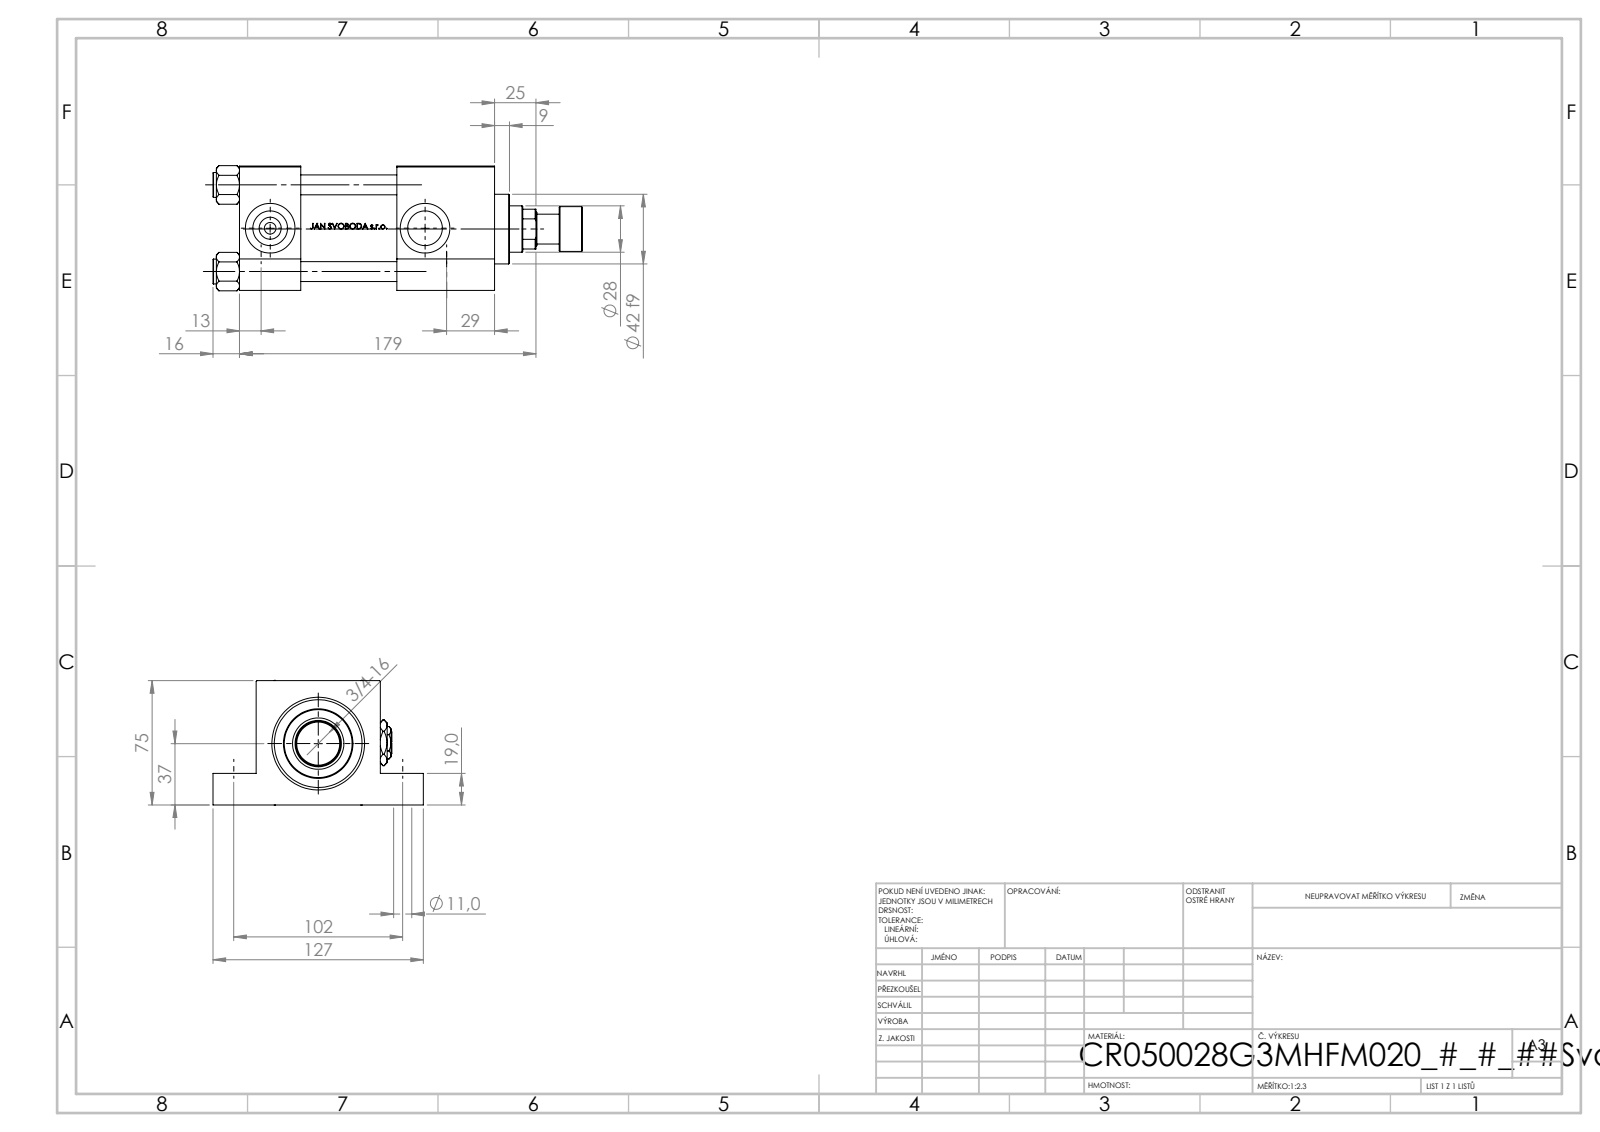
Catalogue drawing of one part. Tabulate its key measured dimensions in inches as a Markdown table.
| quantity | value |
| --- | --- |
| part name | Zatka_pro_OIL_PORT; V215CR_VCP_G; V215CR_ROD_END_F; NUT_M5_G (+3 more) |
| STEP written by | SolidWorks 2019 (CONFIG_CONTROL_DESIGN) |
| units | inches |
| bodies | 14 solids, 1197 faces (481 planar, 136 cylindrical, 580 other) |
| overall size | 8.78 × 5 × 2.974 |
| volume | 47.23 in³ |
| surface area | 264.8 in² |
| round holes (diameter × count) | 0.472 × 4, 0.433 × 3, 0.276 × 2, 0.825 × 2, 1.181 × 2, 0.433 × 1, 0.728 × 1, 1.102 × 1, 1.22 × 1, 1.614 × 1, 1.969 × 1, 2.087 × 1 |
| round bosses / shafts (diameter × count) | 0.591 × 4, 2.205 × 1, 1.654 × 1, 1.063 × 1, 0.709 × 1 |
| main face-to-face distances | 2.953, 1.457, 6.063, 4.606, 0.748, 2.205, 3.74, 2.283, 2.323, 1.024 |
| hole center spacings | 2.059, 1.442, 1.47, 2.912, 4.016, 4.409, 5.964, 3.681 |
